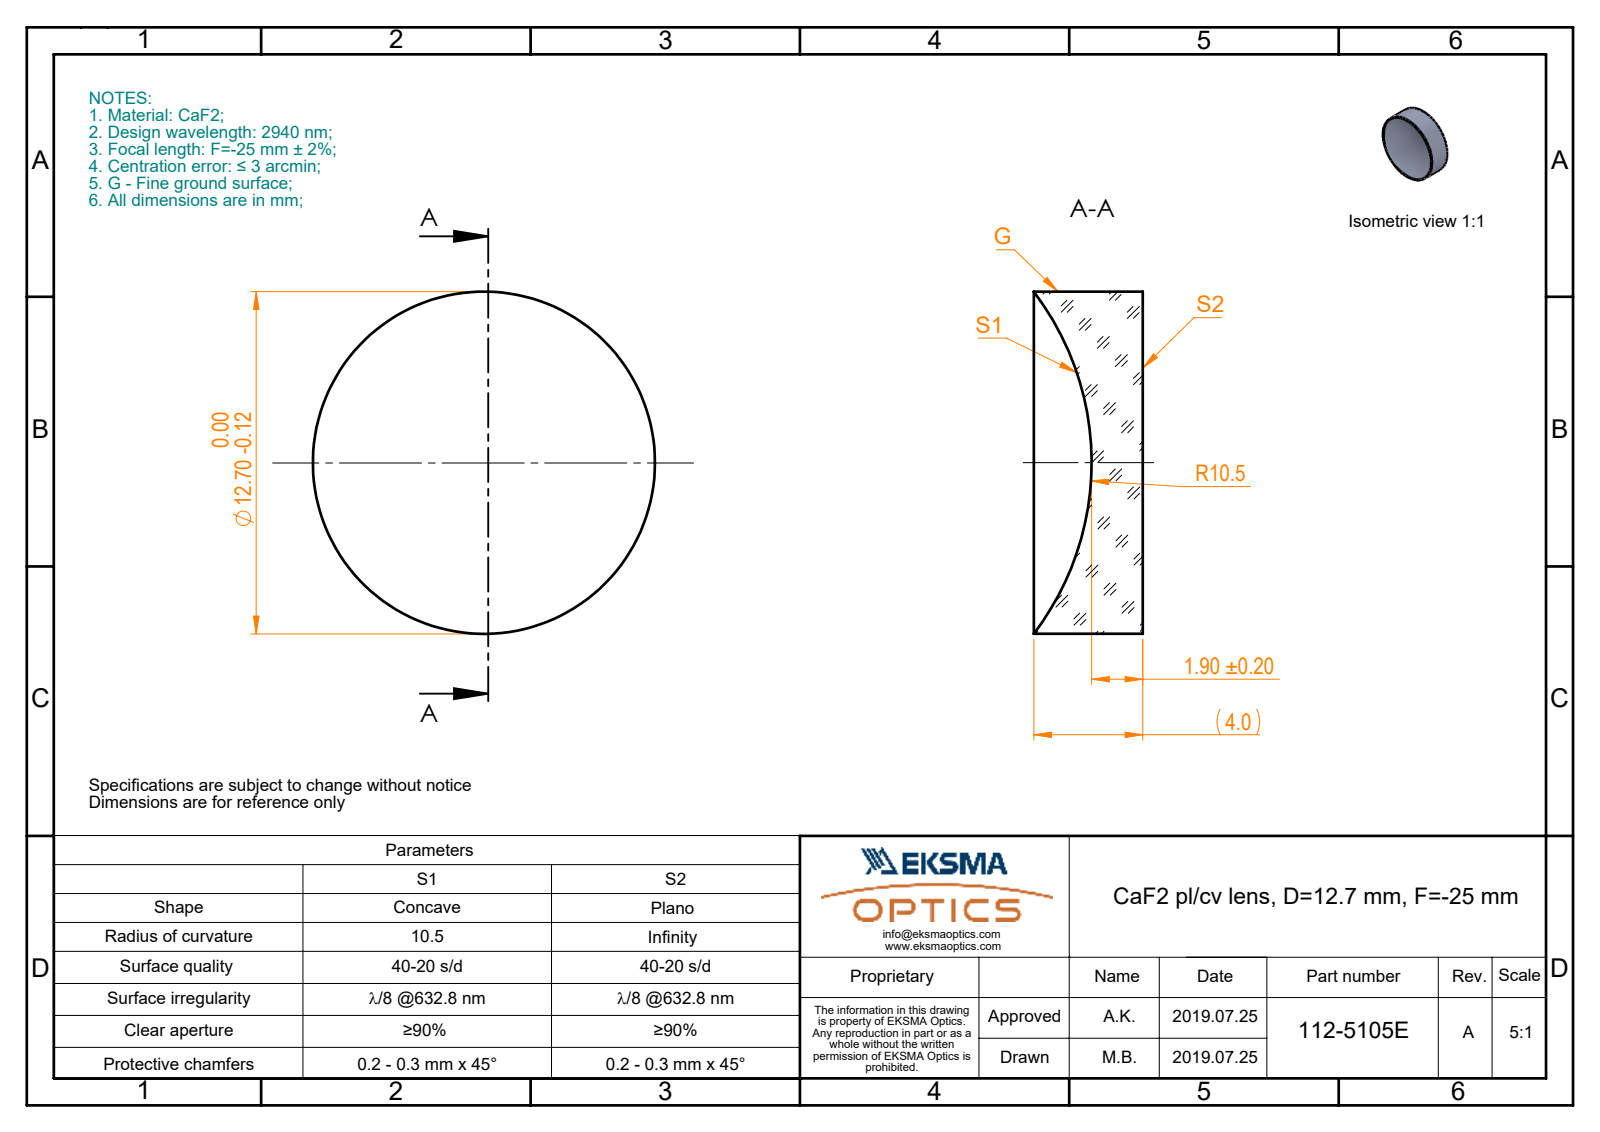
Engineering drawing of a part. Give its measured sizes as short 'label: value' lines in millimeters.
name: 112-5105E CaF2 pl-cv 12.7 F-25
written by: SolidWorks 2017 (CONFIG_CONTROL_DESIGN)
unit: mm
bodies: 1 solid, 5 faces (1 planar, 2 cylindrical, 2 other)
size: 12.7 × 12.7 × 4.05
volume: 372 mm³; area: 429 mm²
bosses: 1× ⌀12.7
